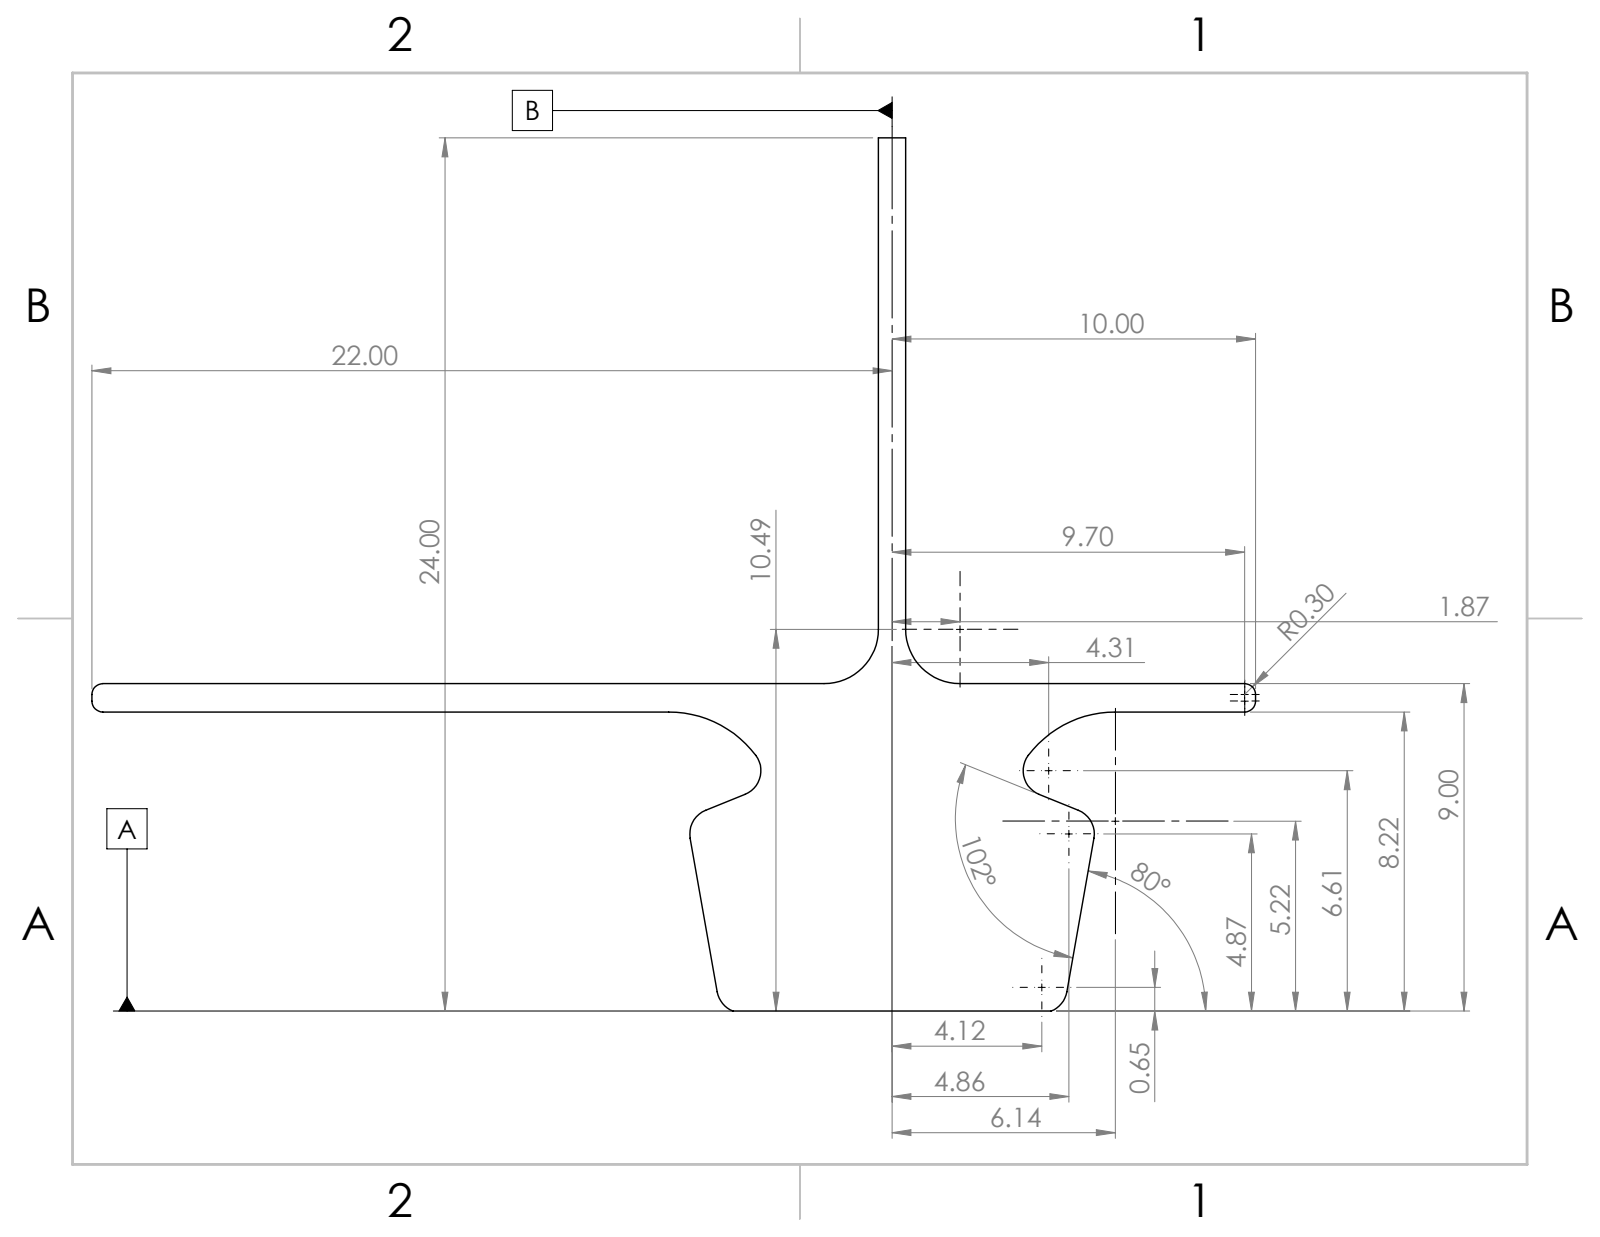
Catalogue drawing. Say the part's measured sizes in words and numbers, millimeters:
The part is named "Concept 4 Flat Pattern". Its 3-D file was written by "SolidWorks 2017 (AUTOMOTIVE_DESIGN)". It is 1 solid with 32 faces: 16 planar, 16 cylindrical and 0 other. Overall it measures 812.8 by 609.6 by 1 millimeters. Its volume is 76 490 cubic millimeters and its surface area 153 500 square millimeters. Partial cylindrical surfaces (rounded edges, fillets, slot ends): 6 of radius 17.8, 4 of radius 7.6, 2 of radius 37.9, 2 of radius 76.2. The main face-to-face distances are 1, 19.8, 19.1, 208.8, 228.6, 609.6, 400.8, 381, 263.4, 244.4.
